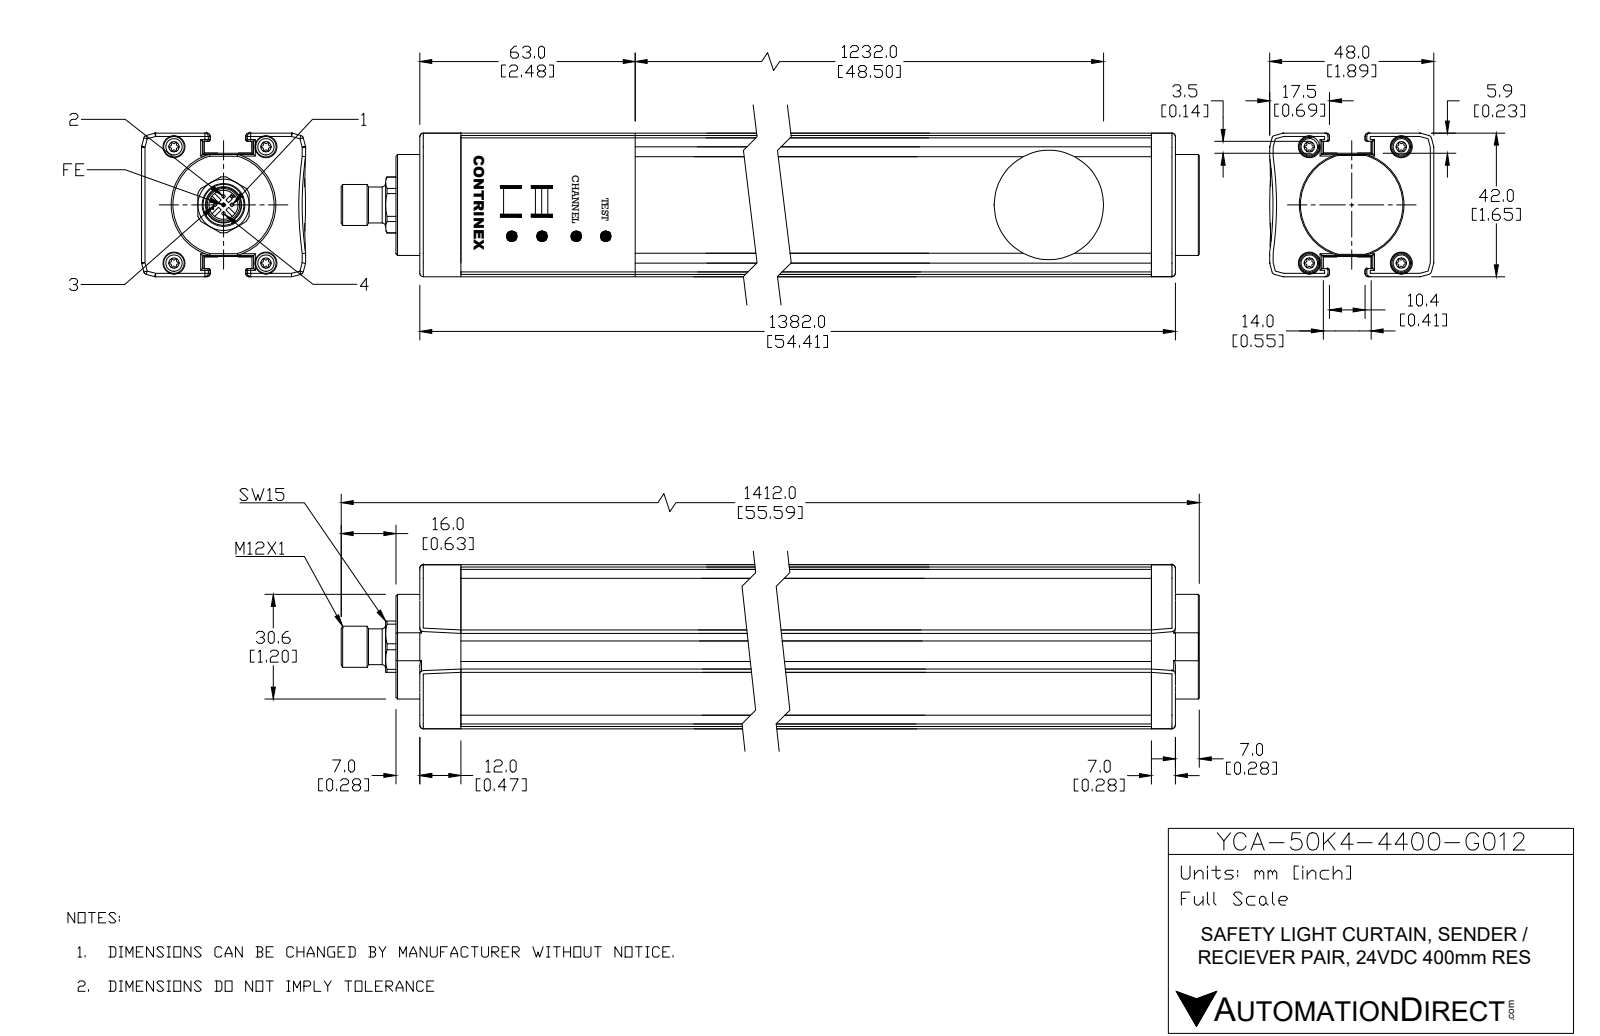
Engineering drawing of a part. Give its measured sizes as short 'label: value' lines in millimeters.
name: YCA-50K4-4400-G012
written by: SolidWorks 2019 (AUTOMOTIVE_DESIGN)
unit: mm
bodies: 1 solid, 533 faces (121 planar, 152 cylindrical, 260 other)
size: 1412 × 48 × 42
volume: 2 325 000 mm³; area: 402 700 mm²
holes: 4× ⌀3, 4× ⌀6, 1× ⌀8.5
bosses: 5× ⌀1, 4× ⌀5.5, 4× ⌀3, 1× ⌀30.6, 1× ⌀12, 1× ⌀10.5
rounds: 36× R0.9, 12× R1, 10× R0.4, 2× R5.5, 1× R0.5, 1× R0.5, 1× R8.2, 1× R17.5
face distances: 5.9, 36.1, 42, 30.3, 46.4, 55.2, 50.9, 5.1, 36.9, 0.8
hole spacings: 21, 22.4, 26.9, 34, 43.4
